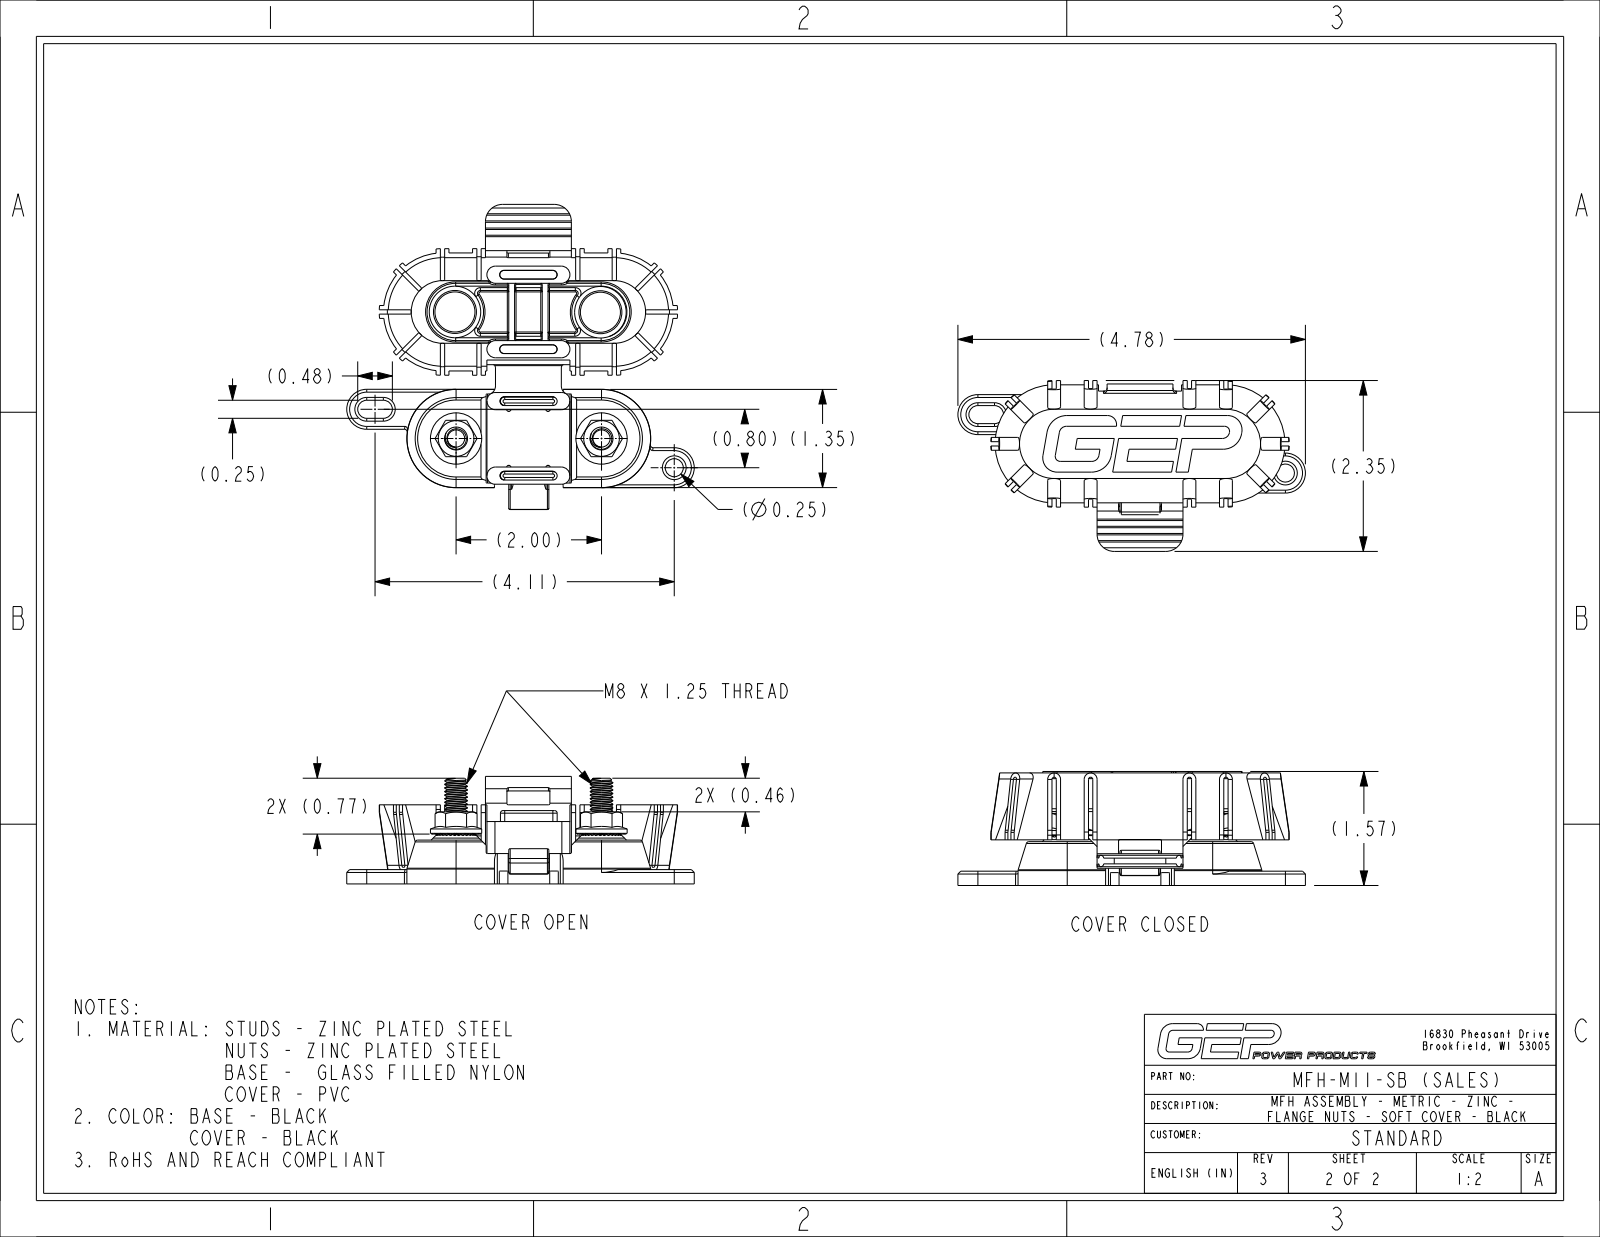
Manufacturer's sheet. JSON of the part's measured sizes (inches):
{"part_name": "MFH-MXX-XX_BODY_NCF; C05-1003-M1_NCF; C02-1005-X_NCF; MFH-SB_NCF_INSTALLED (+1 more)", "step_written_by": "CREO PARAMETRIC BY PTC INC, 2024014 (CONFIG_CONTROL_DESIGN)", "units": "inches", "bodies": {"solids": 6, "faces": 2343, "planar": 929, "cylindrical": 749, "other": 665}, "overall_size": [4.778, 2.348, 1.567], "volume_in3": 3.288, "surface_area_in2": 86.97, "round_holes": [[0.244, 2], [0.354, 2], [0.591, 2], [0.248, 1]], "round_bosses_or_shafts": [[0.705, 2], [0.63, 2], [0.315, 2]], "partial_cylinders_radius": [[0.016, 236], [0.02, 24], [0.039, 20], [0.02, 14], [0.015, 13], [0.012, 10], [0.035, 10], [0.059, 10]], "face_to_face_distances": [0.059, 0.118, 0.079, 0.423, 0.177, 0.945, 1.024, 1.13, 0.02, 0.6], "hole_center_spacings": [2, 1.078, 1.087, 1.991, 2.009, 3.027, 3.036]}
